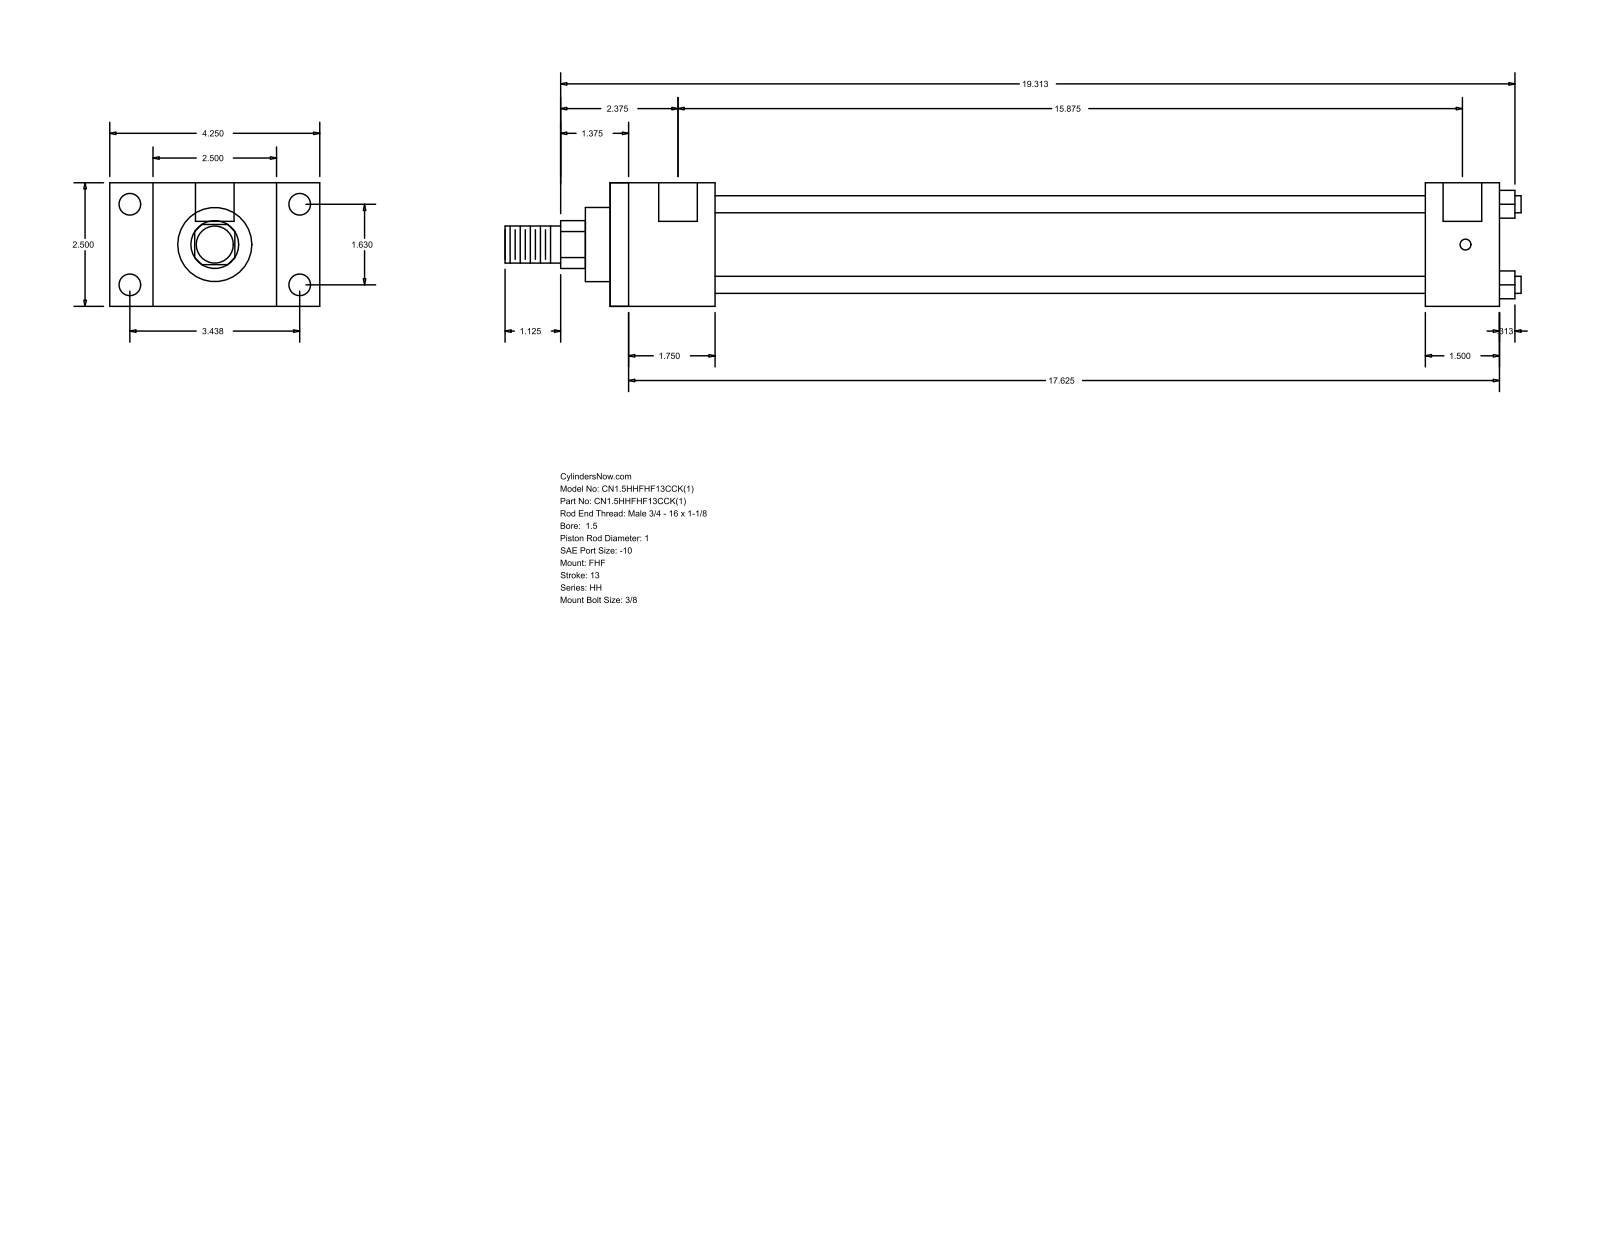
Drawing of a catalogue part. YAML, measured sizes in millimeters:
part_name: "HH_FHF__0150_1"
step_written_by: "GSSL Pune (CONFIG_CONTROL_DESIGN)"
units: millimeters
bodies: {solids: 0, faces: 88, planar: 60, cylindrical: 28, other: 0}
overall_size: [522.29, 107.95, 63.5]
round_holes:
  - {diameter: 5.56, count: 4}
  - {diameter: 11.13, count: 4}
  - {diameter: 19.84, count: 2}
round_bosses_or_shafts:
  - {diameter: 8.76, count: 4}
  - {diameter: 44.45, count: 1}
  - {diameter: 38.1, count: 1}
  - {diameter: 25.4, count: 1}
  - {diameter: 19.05, count: 1}
partial_cylinders:
  - {radius: 12.29, count: 1}
face_to_face_distances: [63.5, 22.23, 85.73, 53.98, 107.96, 457.2, 403.22, 38.1, 419.1, 365.12]
hole_center_spacings: [1.59, 41.4, 87.32, 96.64, 404.81, 406.4, 403.22]
